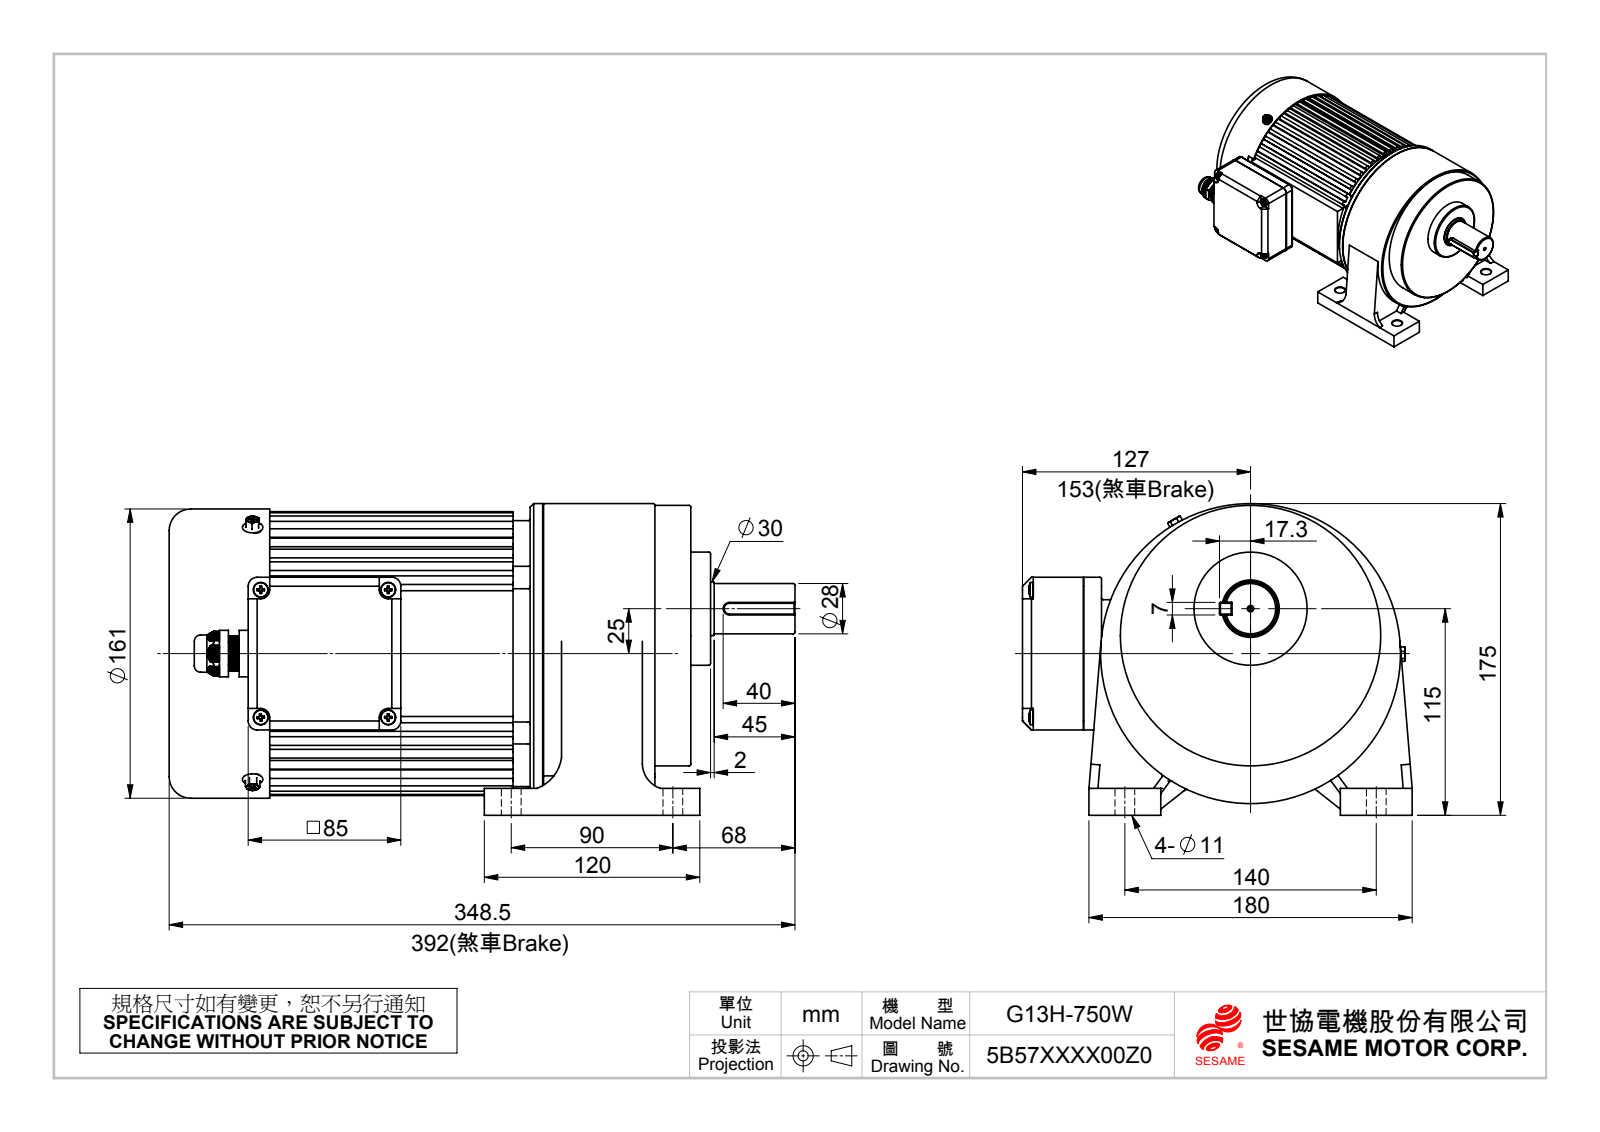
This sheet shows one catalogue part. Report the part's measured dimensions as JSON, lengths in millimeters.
{"part_name": "成品-塑膠T盒; 外六角內十字螺絲M5 x 10_ISO 4162 - M5 x 10 x 10-N; 750後蓋-M-SAB-45_3.烤車鑽; 750W風扇蓋159＊56 (+8 more)", "step_written_by": "SolidWorks 2010 (CONFIG_CONTROL_DESIGN)", "units": "millimeters", "bodies": {"solids": 19, "faces": 3031, "planar": 997, "cylindrical": 939, "other": 1095}, "overall_size": [348.5, 217, 173.5], "volume_mm3": 5631000, "surface_area_mm2": 554441, "round_holes": [[5, 13], [8, 10], [3.3, 9], [4.2, 7], [5.1, 5], [6, 4], [11, 4], [2, 1], [10.8, 1], [16.5, 1], [30, 1], [31, 1]], "round_bosses_or_shafts": [[8.3, 4], [4, 4], [5, 3], [167, 1], [161, 1], [159, 1], [150, 1], [148, 1]], "partial_cylinders_radius": [[1, 65], [2, 46], [3, 8], [5, 8], [0.5, 6], [2.5, 6], [8, 5], [2.55, 4]], "face_to_face_distances": [140, 5, 22, 27, 9.5, 149.5, 162, 128, 77, 12], "hole_center_spacings": [144.57, 45, 64.77, 66, 71, 89.35, 76, 108.92]}
